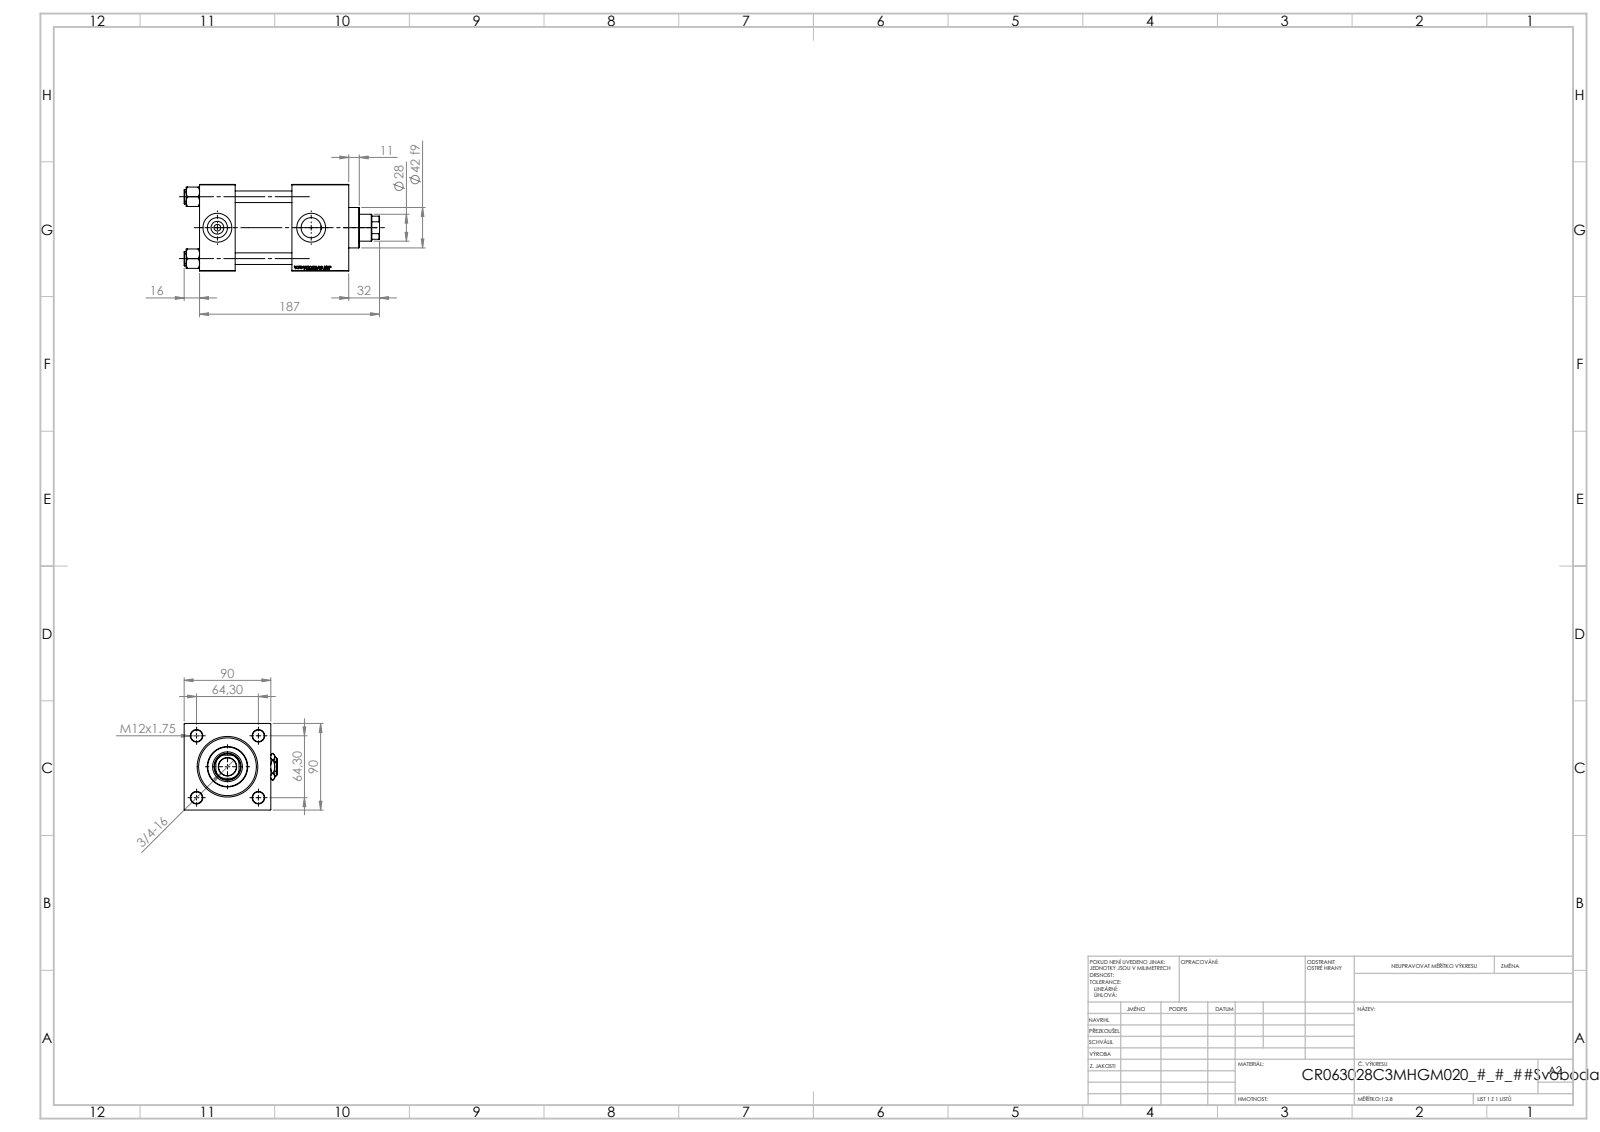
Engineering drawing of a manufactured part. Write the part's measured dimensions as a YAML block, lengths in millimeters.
part_name: "V215CR_C_Body; V215_VC_A; V215CR_VCP_C; Zatka_pro_OIL_PORT (+2 more)"
step_written_by: "SolidWorks 2019 (CONFIG_CONTROL_DESIGN)"
units: millimeters
bodies: {solids: 13, faces: 1250, planar: 574, cylindrical: 98, other: 578}
overall_size: [203, 97, 90]
volume: 940483
surface_area: 183915
round_holes:
  - {diameter: 12, count: 4}
  - {diameter: 7, count: 2}
  - {diameter: 20.96, count: 2}
  - {diameter: 30, count: 2}
  - {diameter: 18.5, count: 1}
  - {diameter: 28, count: 1}
  - {diameter: 31, count: 1}
  - {diameter: 50, count: 1}
  - {diameter: 60, count: 1}
  - {diameter: 63, count: 1}
round_bosses_or_shafts:
  - {diameter: 15, count: 4}
  - {diameter: 69, count: 1}
  - {diameter: 42, count: 1}
partial_cylinders:
  - {radius: 13.5, count: 1}
face_to_face_distances: [90, 59, 37, 118, 155, 96, 126.3, 89.3, 30.3, 28.7]
hole_center_spacings: [45.47, 64.3, 90.93, 97.5]
